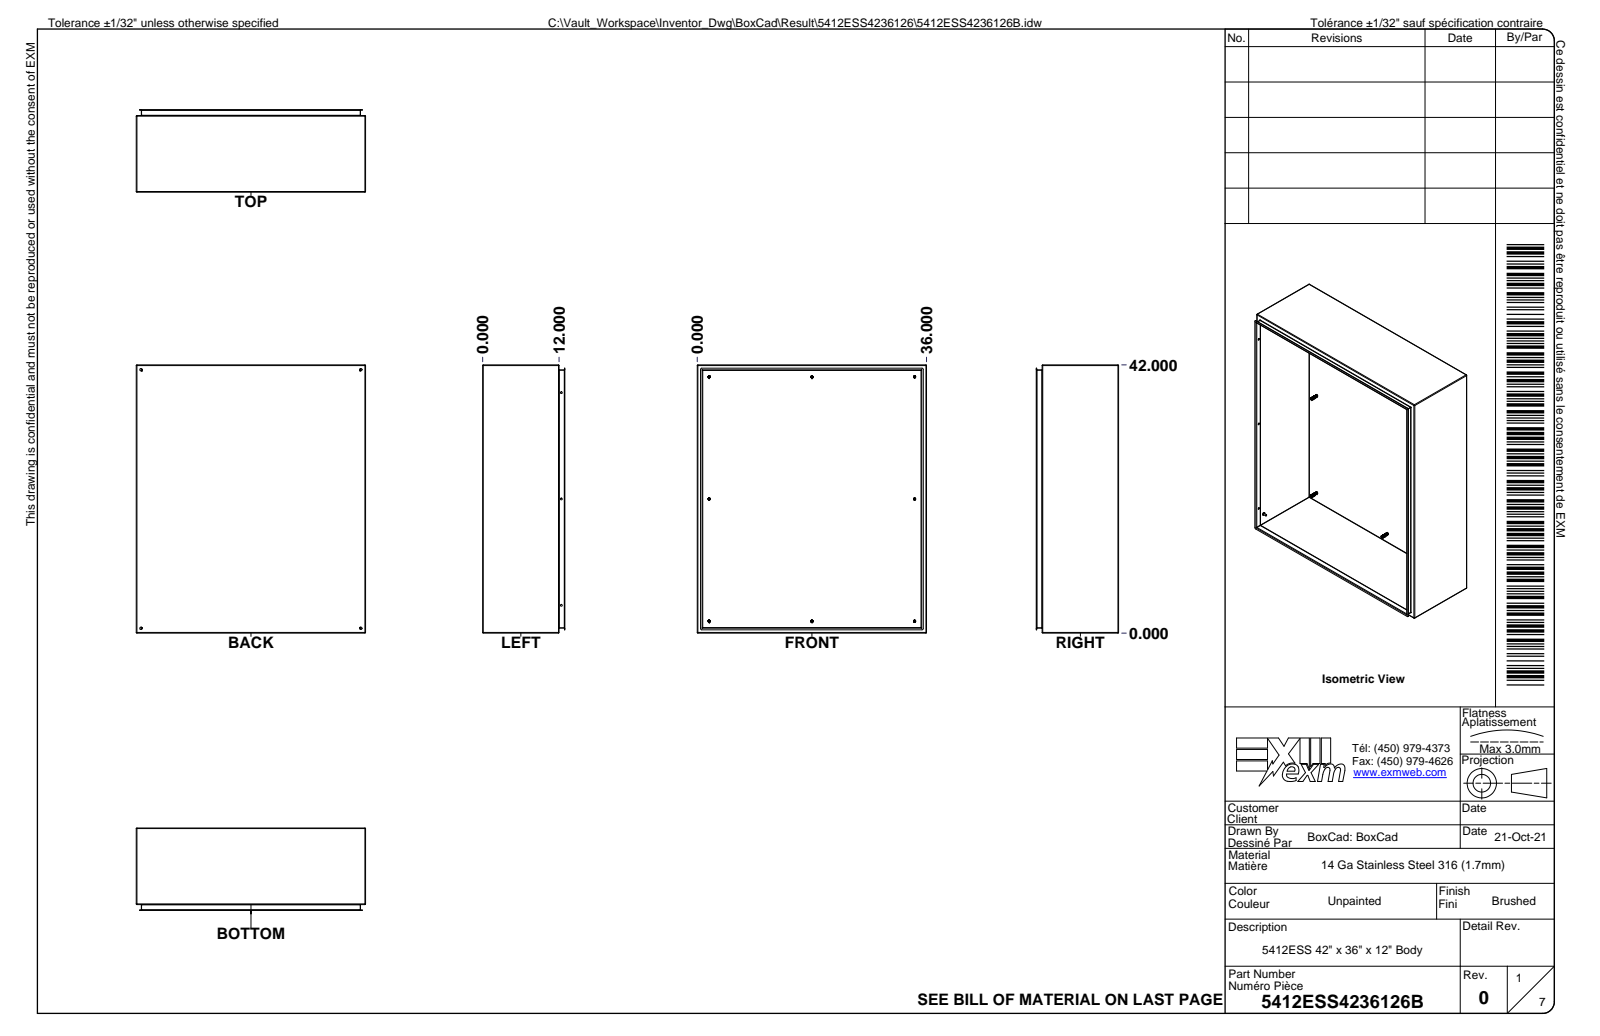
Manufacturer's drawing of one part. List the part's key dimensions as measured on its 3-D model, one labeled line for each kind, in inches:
Part name (STEP PRODUCT): 5412ESS4236126; 5412ESS4236126B; 5412ESS4236126B-P; STK-Q-16020 (+8 more)
STEP written by: Autodesk Inventor 2024 (AUTOMOTIVE_DESIGN)
Units: inches
Bodies: 115 solids, 19259 faces (5812 planar, 4144 cylindrical, 9303 other)
Overall size (bounding box): 42 × 36.007 × 14.985
Volume: 539.2 in³ · Surface area: 14 204 in²
Round holes (diameter × count): ⌀0.165 ×76, ⌀0.03 ×18, ⌀0.315 ×14, ⌀0.201 ×12, ⌀0.311 ×11, ⌀0.27 ×8, ⌀0.29 ×7, ⌀0.044 ×6, ⌀0.197 ×6, ⌀0.268 ×6, ⌀0.5 ×5, ⌀0.39 ×4
Round bosses / shafts (diameter × count): ⌀0.237 ×76, ⌀0.03 ×18, ⌀0.232 ×16, ⌀0.039 ×12, ⌀0.717 ×8, ⌀0.311 ×8, ⌀0.262 ×8, ⌀0.177 ×7
Partial cylindrical surfaces — rounded edges, fillets, slot ends (radius × count): R0.02 ×247, R0.039 ×241, R0.01 ×170, R0.008 ×104, R0.079 ×55, R0.016 ×37, R0.012 ×36, R0.059 ×36
Main face-to-face distances: 0.068, 13.052, 12.984, 13.12, 12.178, 0.942, 0.874, 12.11, 0.105, 1.047
Hole centre spacings: 1.969, 0.984, 2.953, 3.937, 16.652, 4.921, 1.591, 5.906
